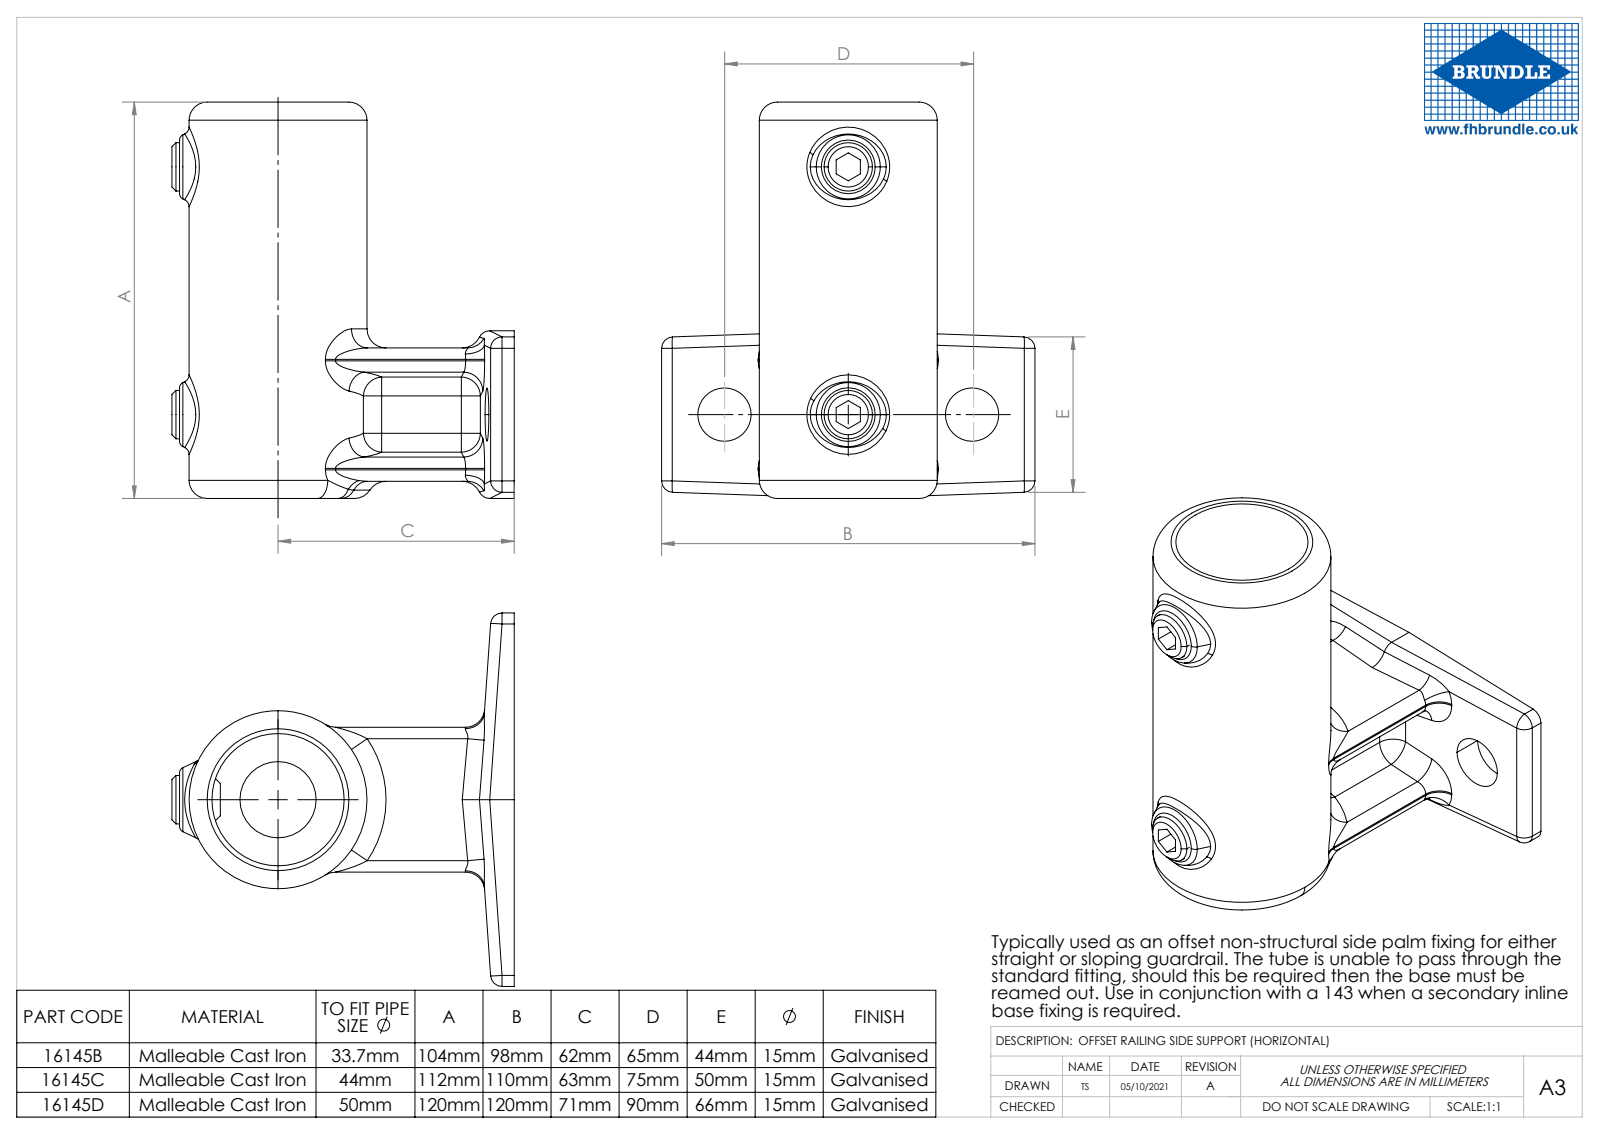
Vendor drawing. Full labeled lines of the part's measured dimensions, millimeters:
Part name (STEP PRODUCT): 16145D
STEP written by: SolidWorks 2020 (CONFIG_CONTROL_DESIGN)
Units: millimetres
Bodies: 1 solid, 150 faces (26 planar, 58 cylindrical, 66 other)
Overall size (bounding box): 120 × 120 × 105
Volume: 217 031 mm³ · Surface area: 72 746 mm²
Round holes (diameter × count): ⌀14 ×2, ⌀15 ×2, ⌀37 ×1, ⌀50 ×1
Round bosses / shafts (diameter × count): ⌀60 ×1
Partial cylindrical surfaces — rounded edges, fillets, slot ends (radius × count): R1 ×30, R2 ×10
Main face-to-face distances: 8, 65, 40.17, 5, 2.5, 67.5, 62.5, 25, 30, 120
Hole centre spacings: 48.1, 80.71, 84, 90
